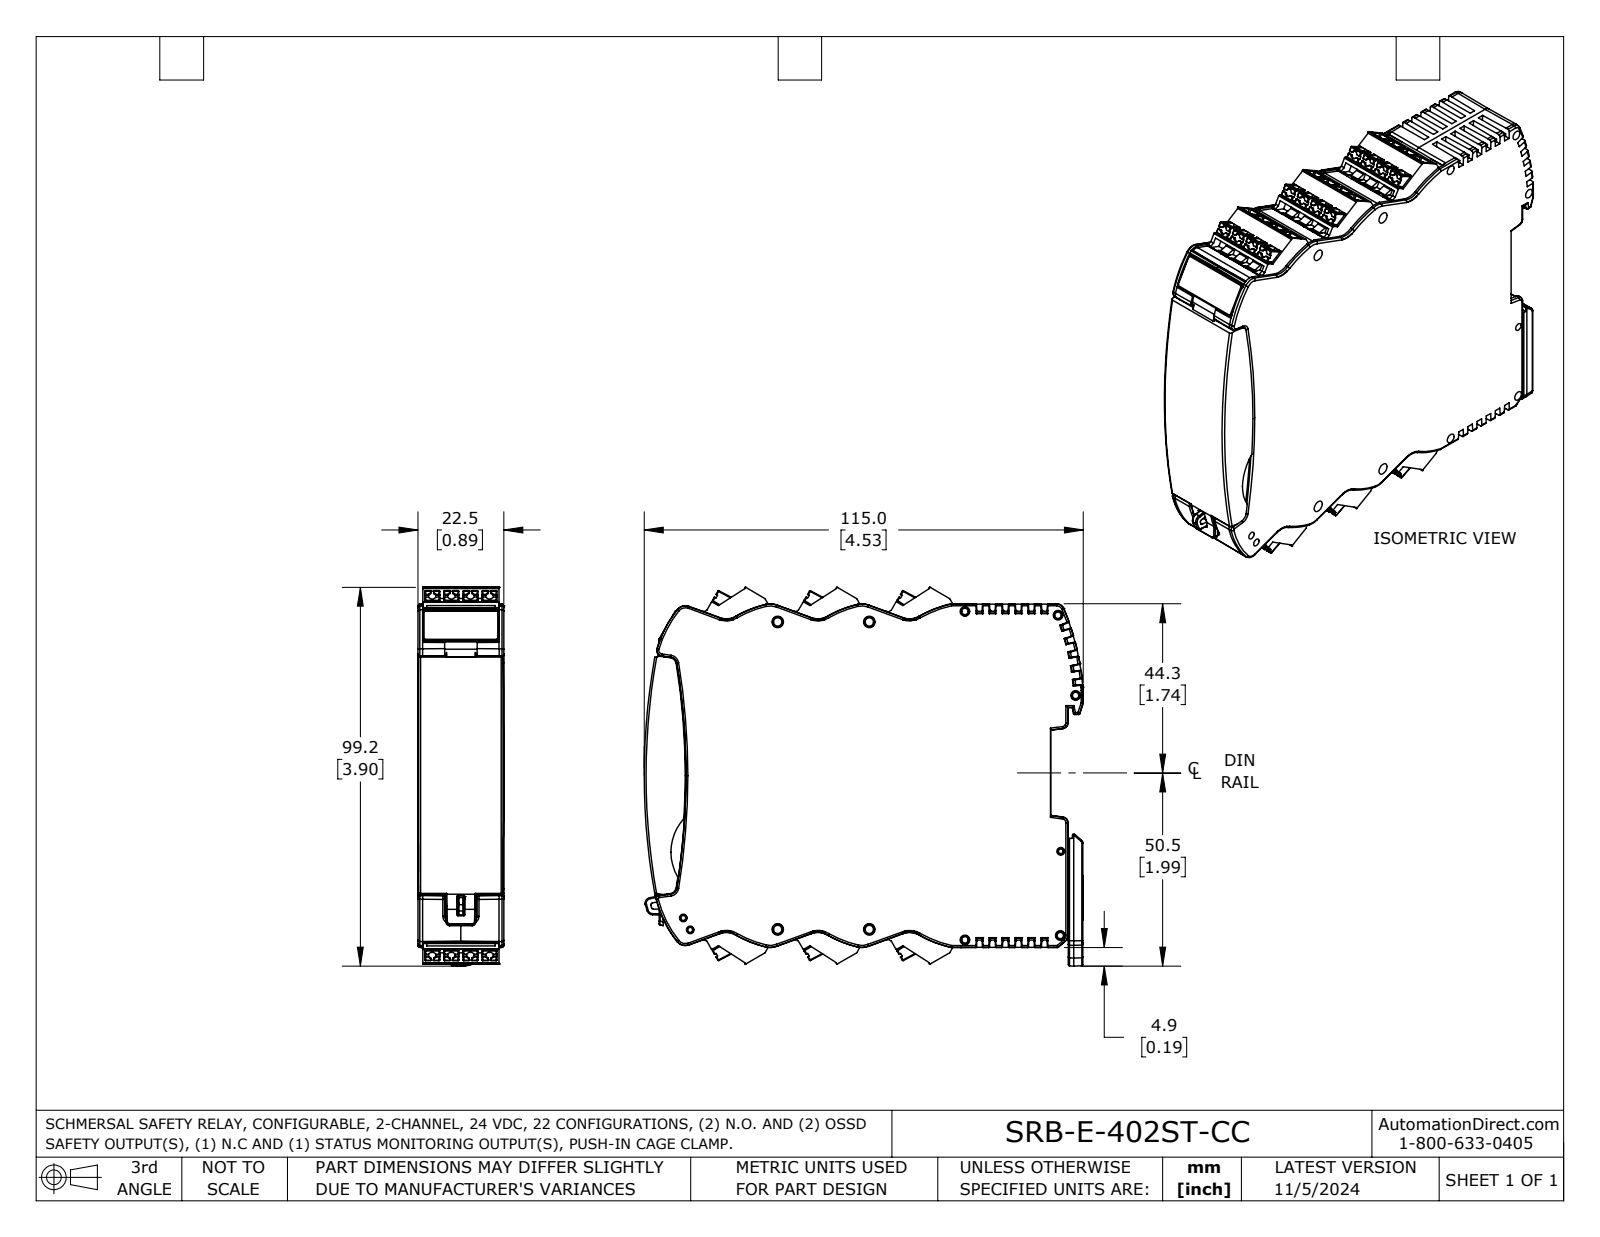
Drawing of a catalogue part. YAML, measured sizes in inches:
part_name: "SRB-E-402ST-CC"
step_written_by: "SolidWorks 2023 (AUTOMOTIVE_DESIGN)"
units: inches
bodies: {solids: 2, faces: 5025, planar: 2673, cylindrical: 1504, other: 848}
overall_size: [4.528, 3.904, 0.886]
volume: 13.03
surface_area: 70.17
round_bosses_or_shafts:
  - {diameter: 0.067, count: 1}
partial_cylinders:
  - {radius: 0.008, count: 297}
  - {radius: 0.012, count: 265}
  - {radius: 0.02, count: 219}
  - {radius: 0.004, count: 66}
  - {radius: 0.039, count: 40}
  - {radius: 0.01, count: 36}
  - {radius: 0.059, count: 26}
  - {radius: 0.047, count: 24}
face_to_face_distances: [0.886, 0.133, 0.197, 0.124, 0.05, 0.785, 0.05, 0.267, 0.035, 0.134]
